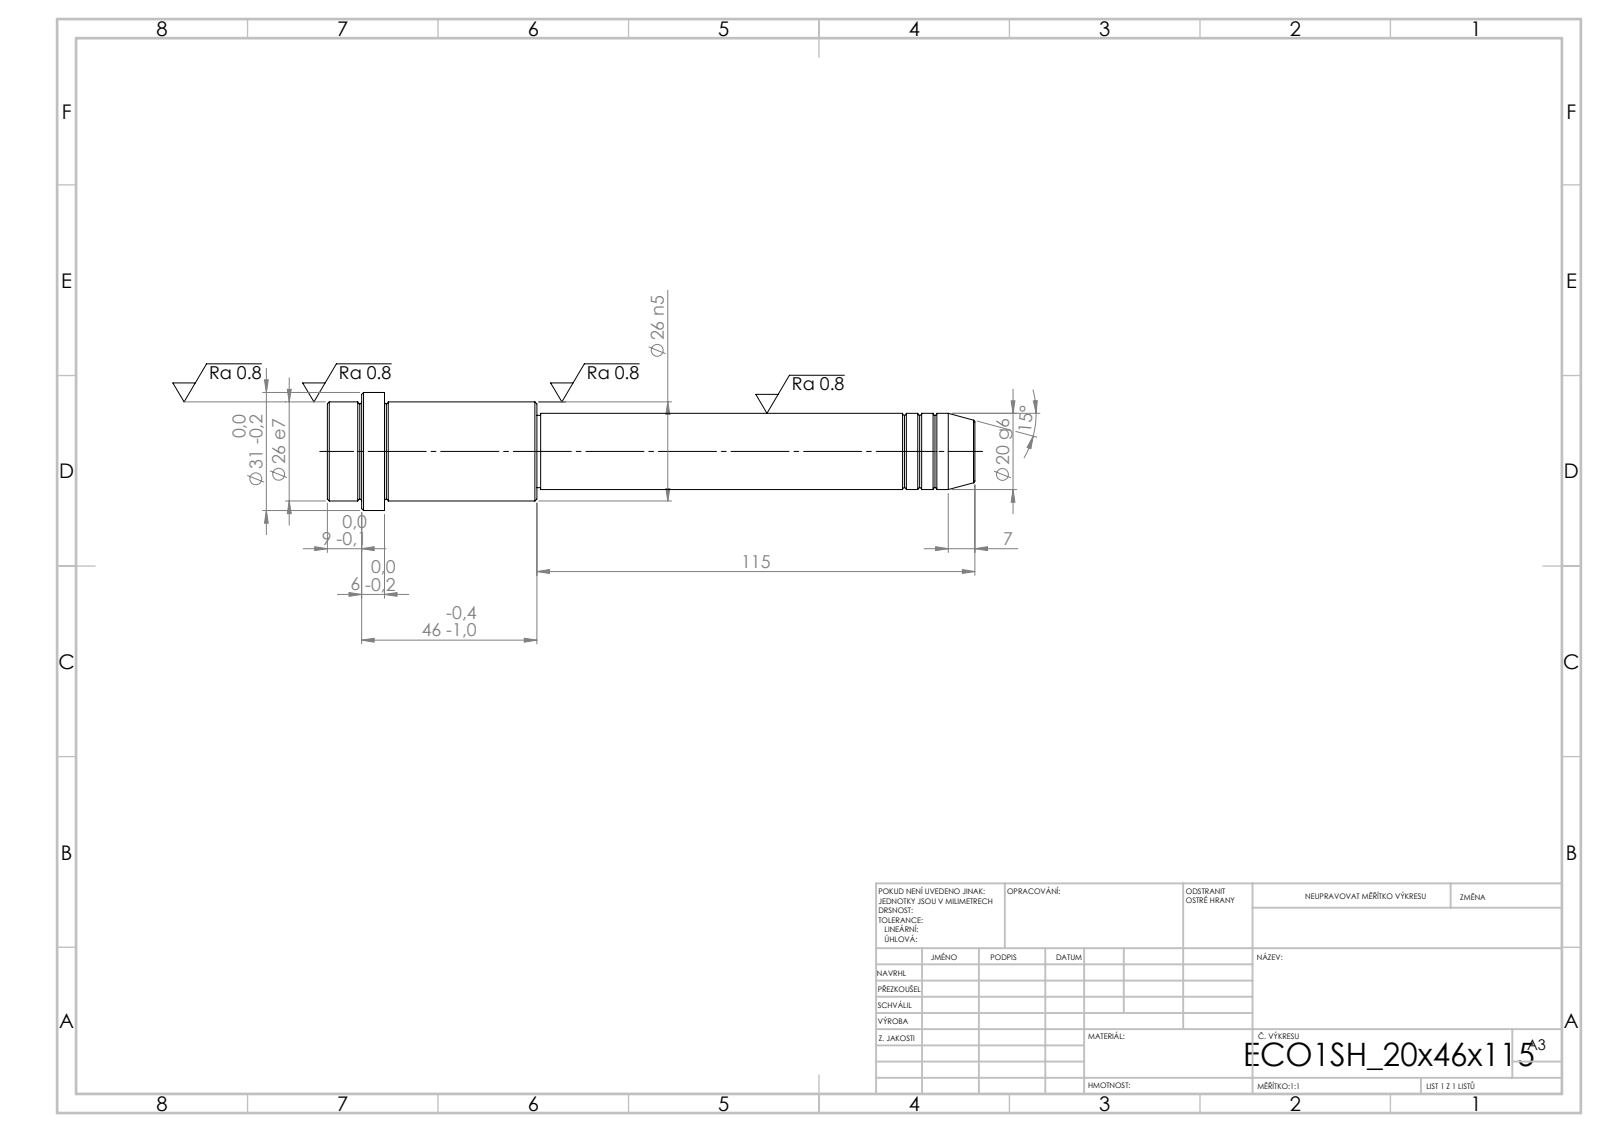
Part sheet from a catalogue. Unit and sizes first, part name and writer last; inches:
Units: inches
Overall size (bounding box): 6.693 × 1.22 × 1.22
Round bosses / shafts (diameter × count): ⌀1.22 ×1, ⌀1.024 ×1, ⌀0.787 ×1, ⌀0.748 ×1
Main face-to-face distances: 0.591, 1.575, 2.165, 4.528, 6.102, 6.693, 6.339, 1.811, 0.236, 0.354
Volume: 4.033 in³ · Surface area: 20.69 in²
Bodies: 1 solid, 52 faces (6 planar, 16 cylindrical, 30 other)
STEP written by: SolidWorks 2019 (CONFIG_CONTROL_DESIGN)
